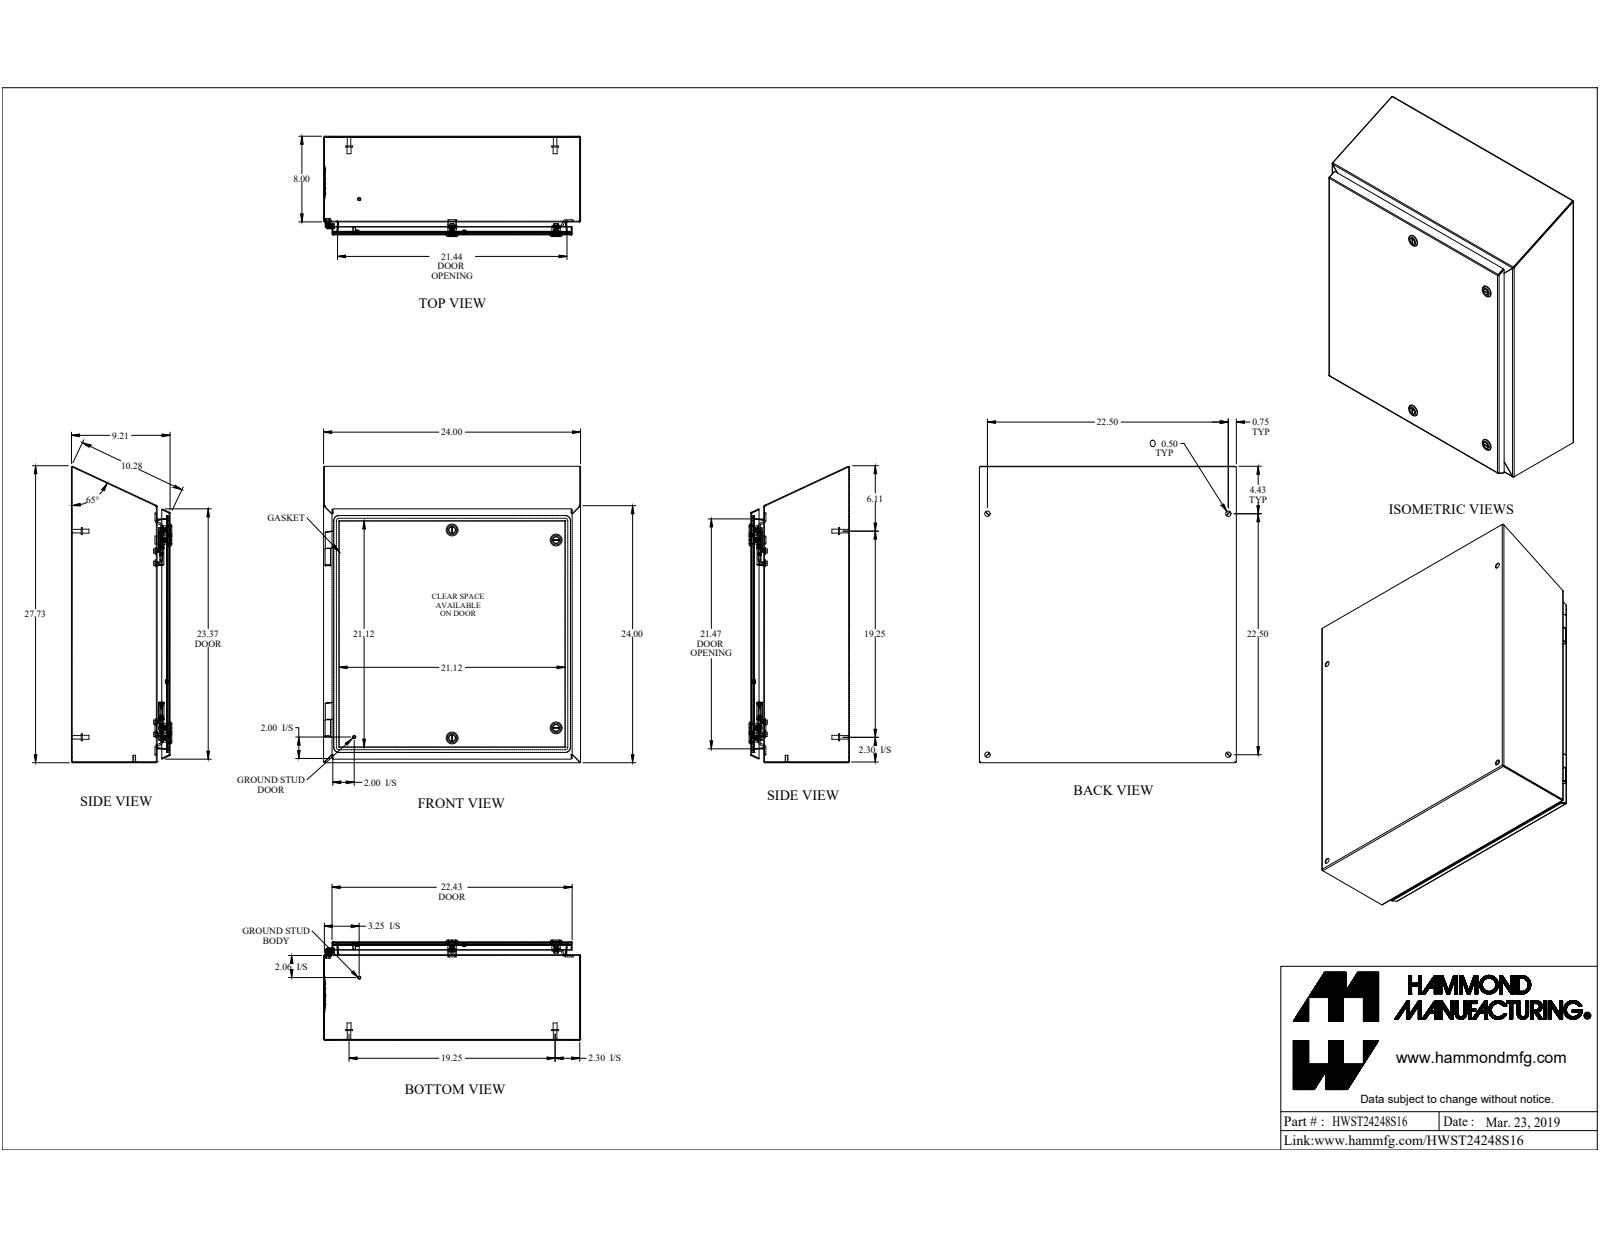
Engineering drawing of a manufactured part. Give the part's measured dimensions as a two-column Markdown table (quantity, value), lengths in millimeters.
| quantity | value |
| --- | --- |
| part name | HWST24248S16 |
| STEP written by | SolidWorks 2019 (AUTOMOTIVE_DESIGN) |
| units | millimeters |
| bodies | 53 solids, 1241 faces (779 planar, 346 cylindrical, 116 other) |
| overall size | 703.2 × 609.6 × 238 |
| volume | 3 000 000 mm³ |
| surface area | 3 193 000 mm² |
| round holes (diameter × count) | 12.7 × 8, 4.9 × 4, 4.9 × 4, 5 × 4, 6.1 × 4, 7 × 4, 9.8 × 4, 16 × 4, 19.5 × 4, 3.3 × 2, 6.1 × 1, 88.9 × 1 |
| round bosses / shafts (diameter × count) | 15.9 × 8, 5.7 × 8, 6 × 5, 27.9 × 4, 16.5 × 4, 13.3 × 4, 9.5 × 4, 8.4 × 4 |
| partial cylindrical surfaces (radius × count) | 6.4 × 24, 1 × 16, 2.7 × 16, 3.2 × 16, 0.8 × 14, 0.3 × 12, 0.9 × 12, 2.7 × 9 |
| main face-to-face distances | 1.8, 230.3, 232.1, 1.8, 232.1, 233.9, 607.8, 201.4, 605.9, 609.6 |
| hole center spacings | 29, 405.9, 571.5, 247.9, 288.3, 288.5, 376.9, 405.9 |
